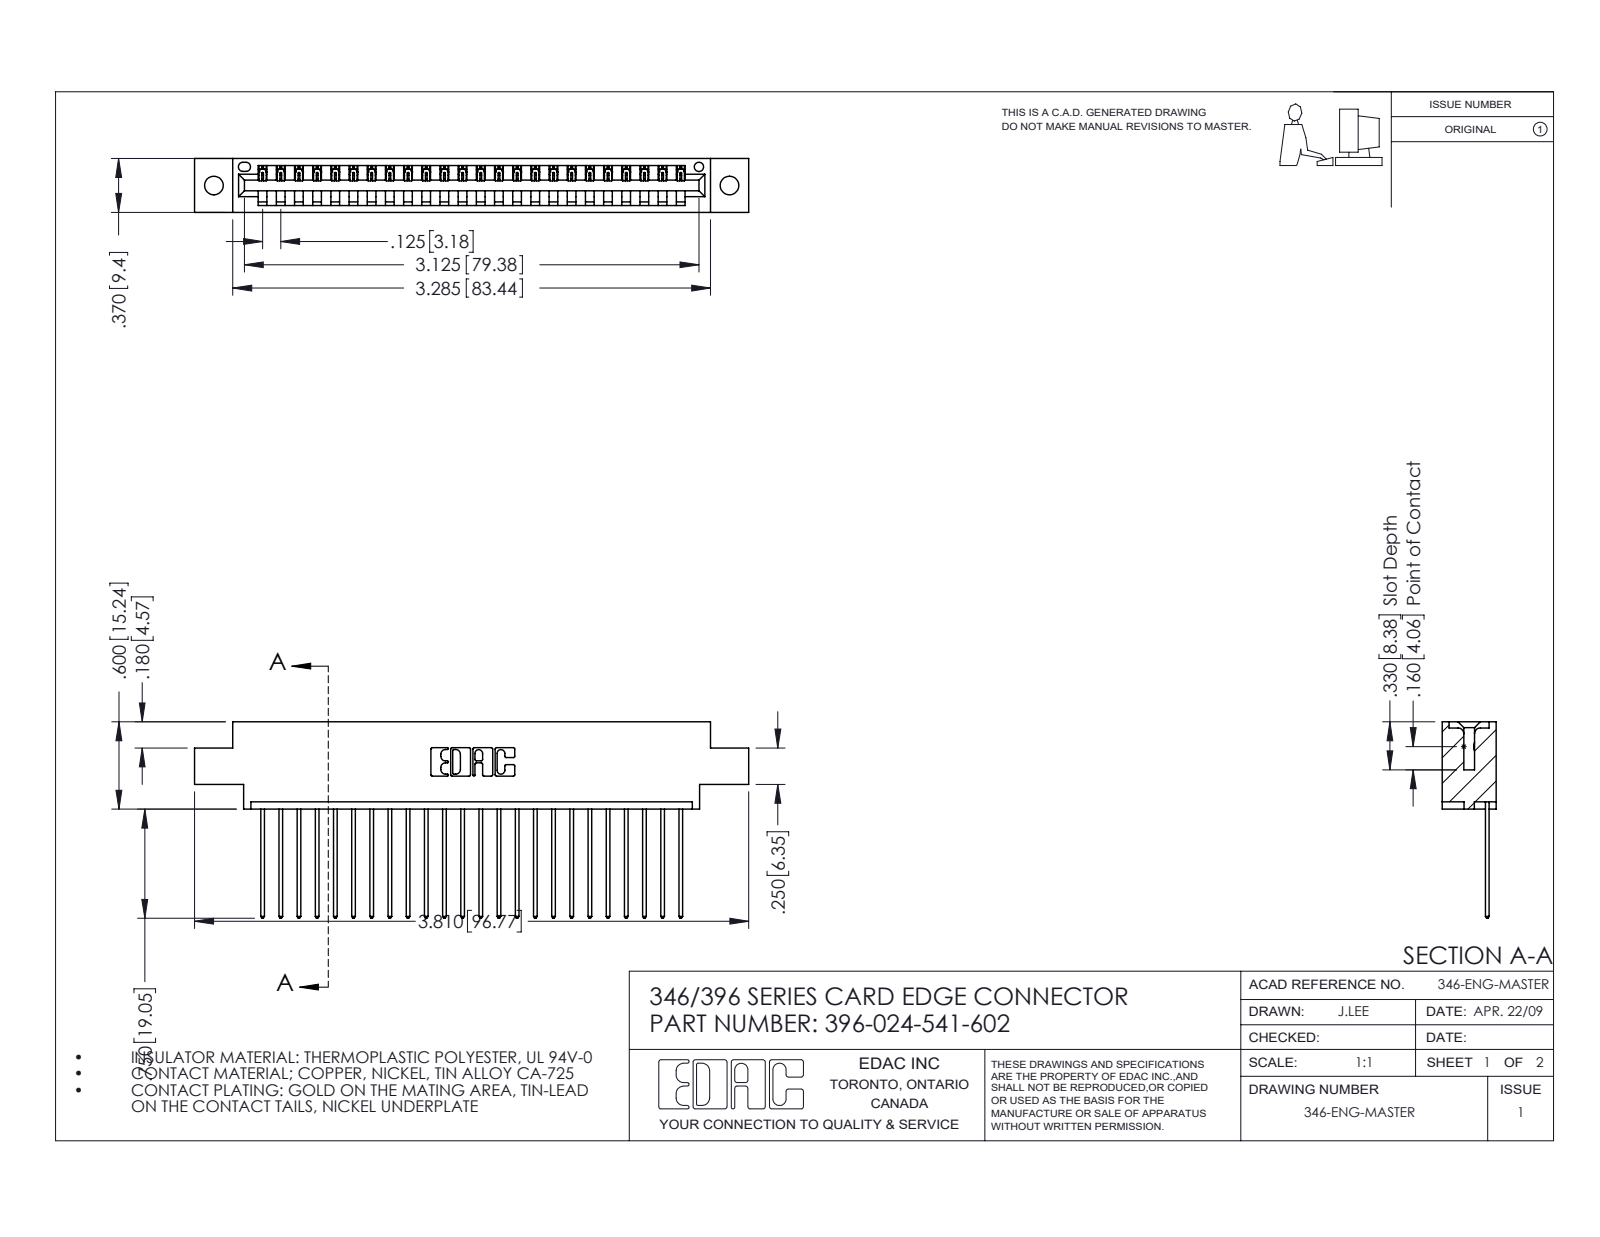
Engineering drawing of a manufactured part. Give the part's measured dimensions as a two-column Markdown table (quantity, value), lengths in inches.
| quantity | value |
| --- | --- |
| part name | 346 Part_0.170 Offset - 0.128 Dia; 396-024-541-602; 345-292-001_345-293-141 |
| STEP written by | SolidWorks 2016 (CONFIG_CONTROL_DESIGN) |
| units | inches |
| bodies | 25 solids, 1518 faces (1040 planar, 478 cylindrical, 0 other) |
| overall size | 3.81 × 1.35 × 0.37 |
| volume | 0.551 in³ |
| surface area | 17.75 in² |
| round holes (diameter × count) | 0.128 × 2, 0.064 × 1 |
| partial cylindrical surfaces (radius × count) | 0.006 × 48, 0.01 × 48, 0.01 × 22, 0.007 × 6, 0.031 × 6, 0.026 × 3, 0.031 × 2, 0.04 × 2 |
| main face-to-face distances | 0.048, 0.322, 0.37, 0.25, 0.072, 0.298, 0.025, 0.148, 0.222, 0.1 |
| hole center spacings | 0.246, 3.337, 3.545 |
